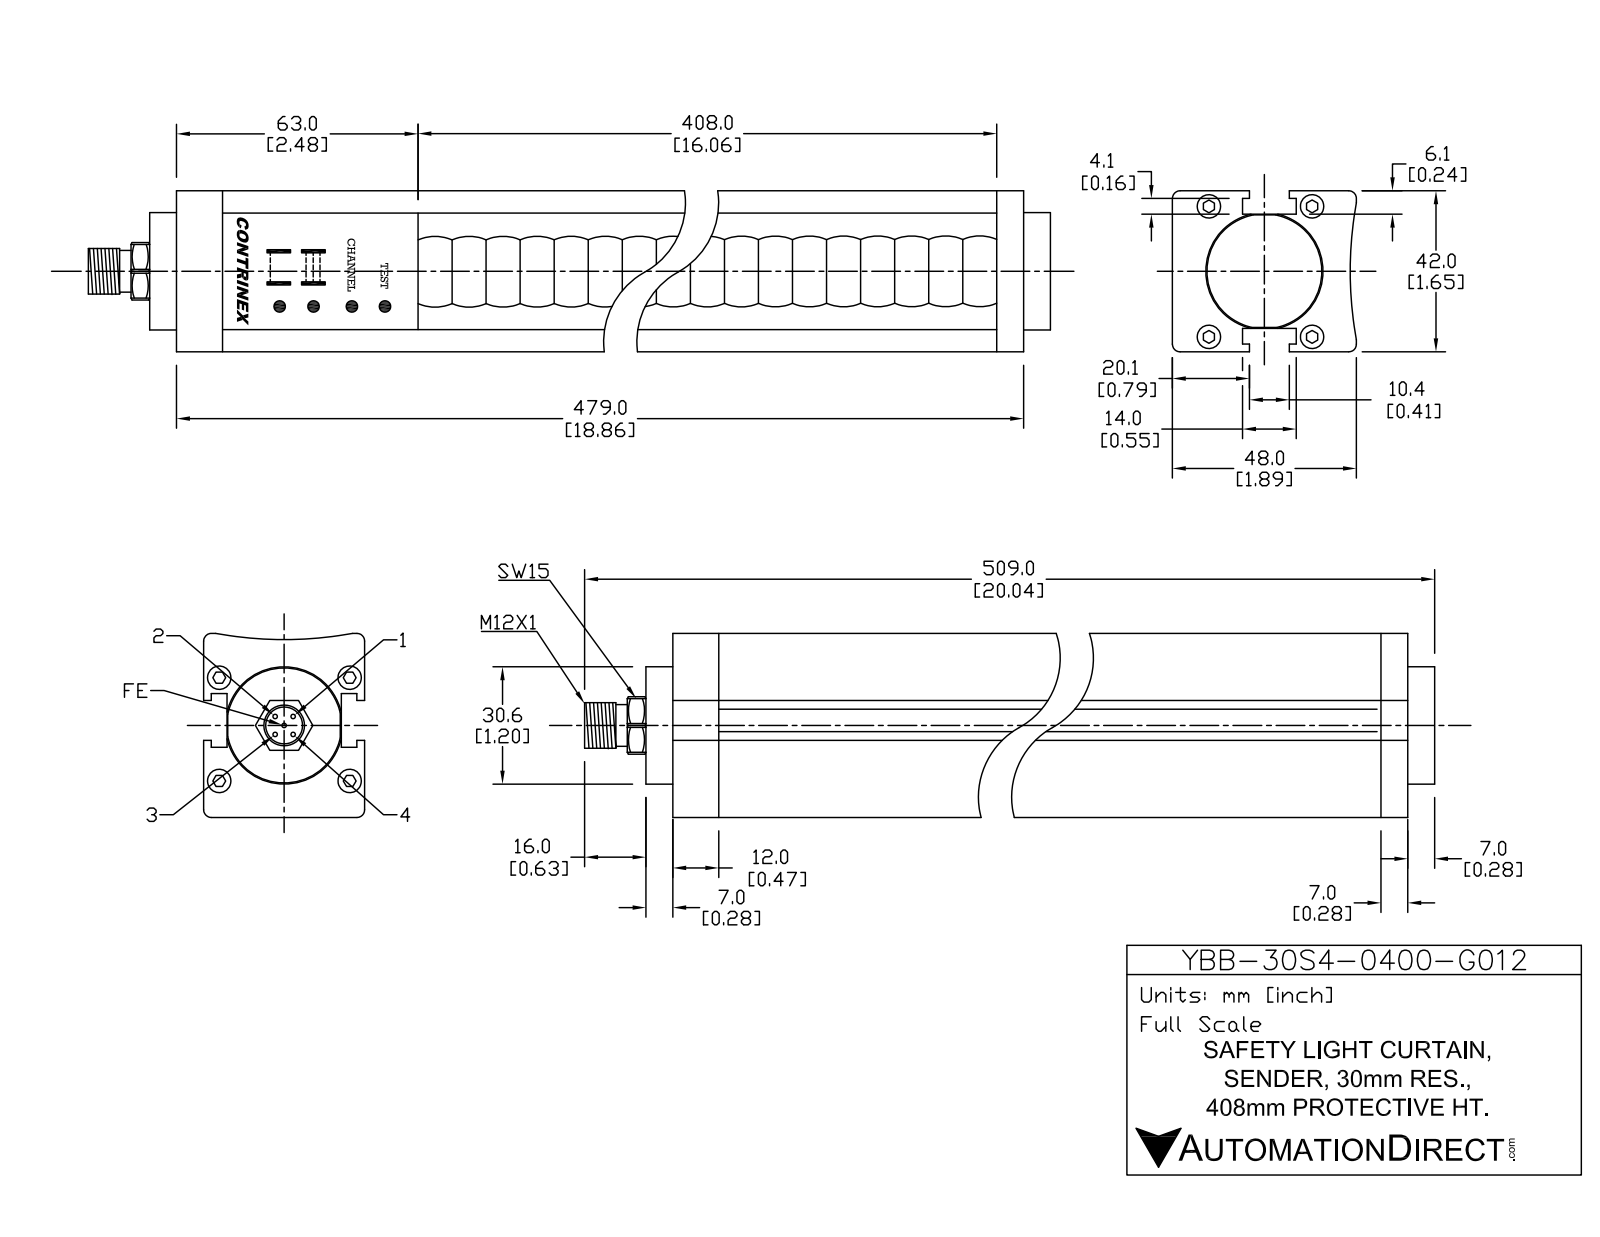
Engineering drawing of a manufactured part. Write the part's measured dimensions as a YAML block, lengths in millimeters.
part_name: "YBB-30S4-0400-G012"
step_written_by: "SolidWorks 2016 (AUTOMOTIVE_DESIGN)"
units: millimeters
bodies: {solids: 19, faces: 440, planar: 208, cylindrical: 168, other: 64}
overall_size: [509, 48, 42]
volume: 868060
surface_area: 119957
round_holes:
  - {diameter: 6, count: 4}
  - {diameter: 8.5, count: 1}
  - {diameter: 32, count: 1}
round_bosses_or_shafts:
  - {diameter: 1, count: 5}
  - {diameter: 5.5, count: 4}
  - {diameter: 30.6, count: 1}
  - {diameter: 12, count: 1}
  - {diameter: 10.5, count: 1}
partial_cylinders:
  - {radius: 1, count: 48}
  - {radius: 0.5, count: 4}
  - {radius: 0.55, count: 2}
  - {radius: 8.2, count: 1}
  - {radius: 100, count: 1}
face_to_face_distances: [6.3, 35.7, 42, 29.4, 14, 17.2, 31.2, 459, 15.7, 29.7]
hole_center_spacings: [21.04, 22.34, 26.9, 34, 43.35]
